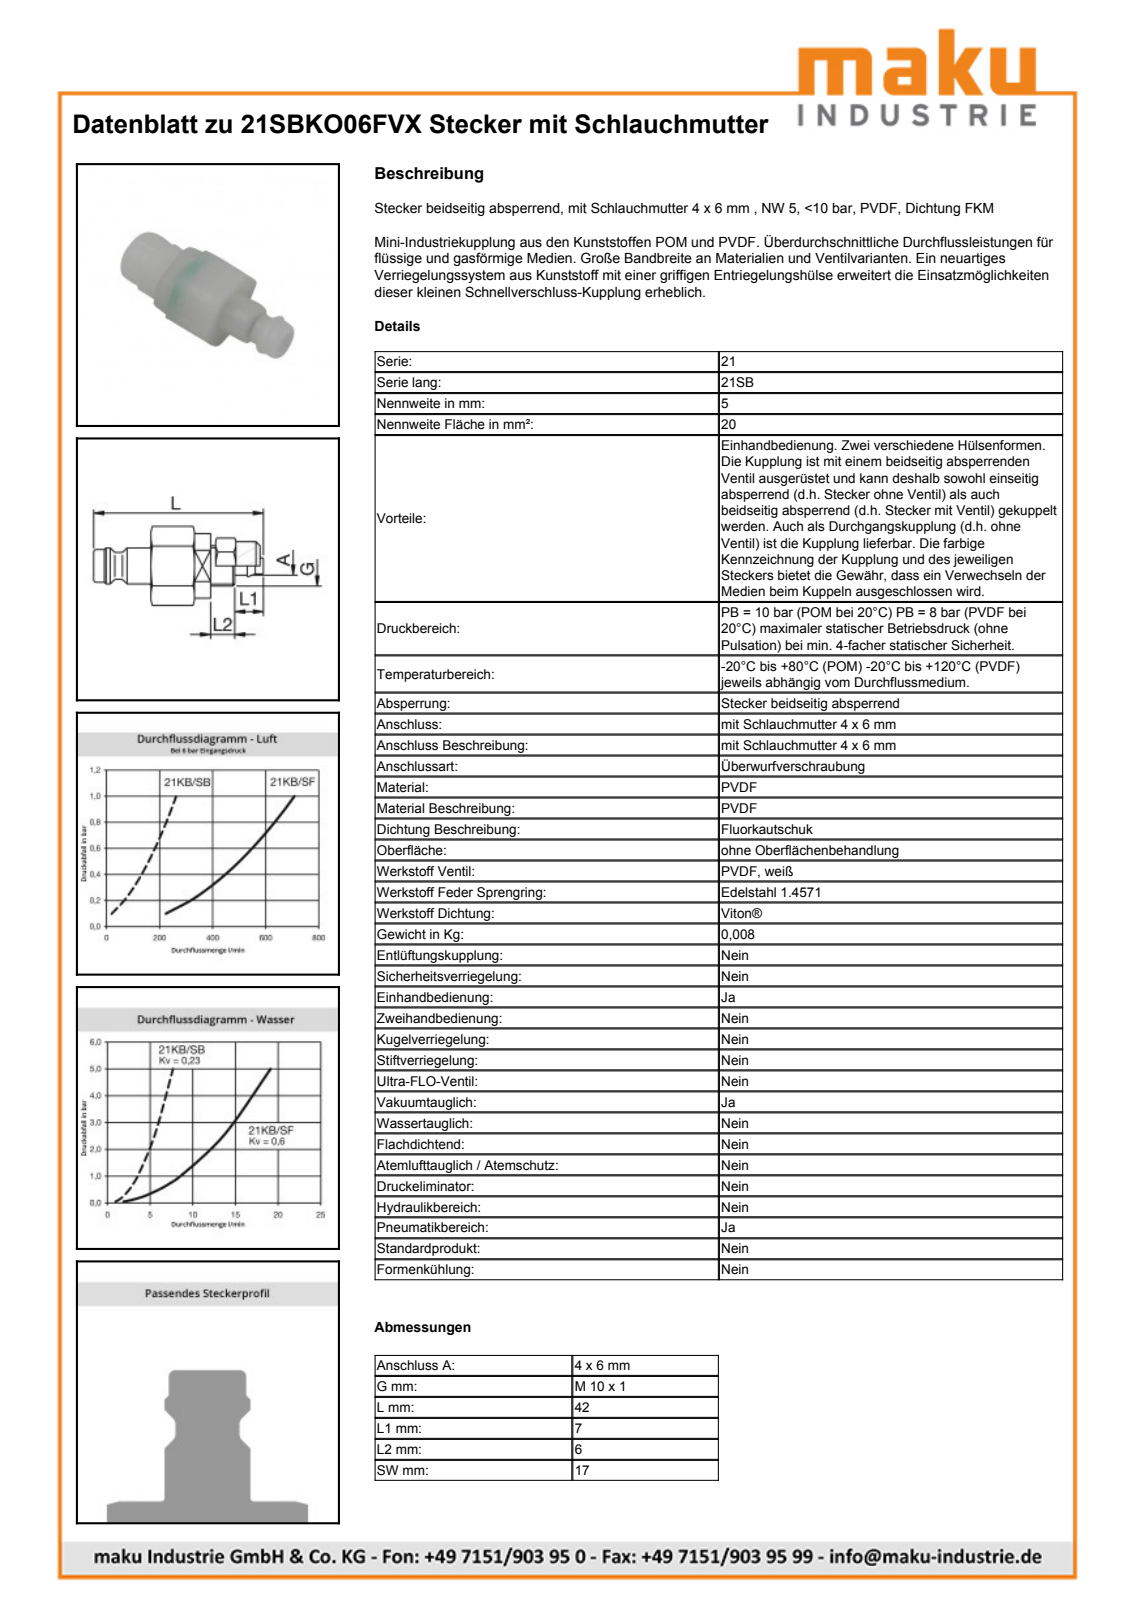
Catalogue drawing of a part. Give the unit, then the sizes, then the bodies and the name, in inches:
Units: inches
Overall size (bounding box): 1.665 × 0.773 × 0.669
Round holes (diameter × count): ⌀0.236 ×1, ⌀0.325 ×1, ⌀0.43 ×1, ⌀0.451 ×1, ⌀0.524 ×1
Round bosses / shafts (diameter × count): ⌀0.472 ×1, ⌀0.413 ×1, ⌀0.354 ×1, ⌀0.348 ×1, ⌀0.326 ×1, ⌀0.321 ×1, ⌀0.264 ×1, ⌀0.262 ×1
Partial cylindrical surfaces — rounded edges, fillets, slot ends (radius × count): R0.197 ×18, R0.315 ×1
Main face-to-face distances: 0.669, 0.551, 0.427, 0.157, 0.585, 0.829, 0.402, 0.244, 1.065, 0.638
Volume: 0.346 in³ · Surface area: 5.169 in²
Bodies: 1 solid, 95 faces (29 planar, 36 cylindrical, 30 other)
Part name (STEP PRODUCT): D114866
STEP written by: Autodesk Inventor 2013 (AUTOMOTIVE_DESIGN)
